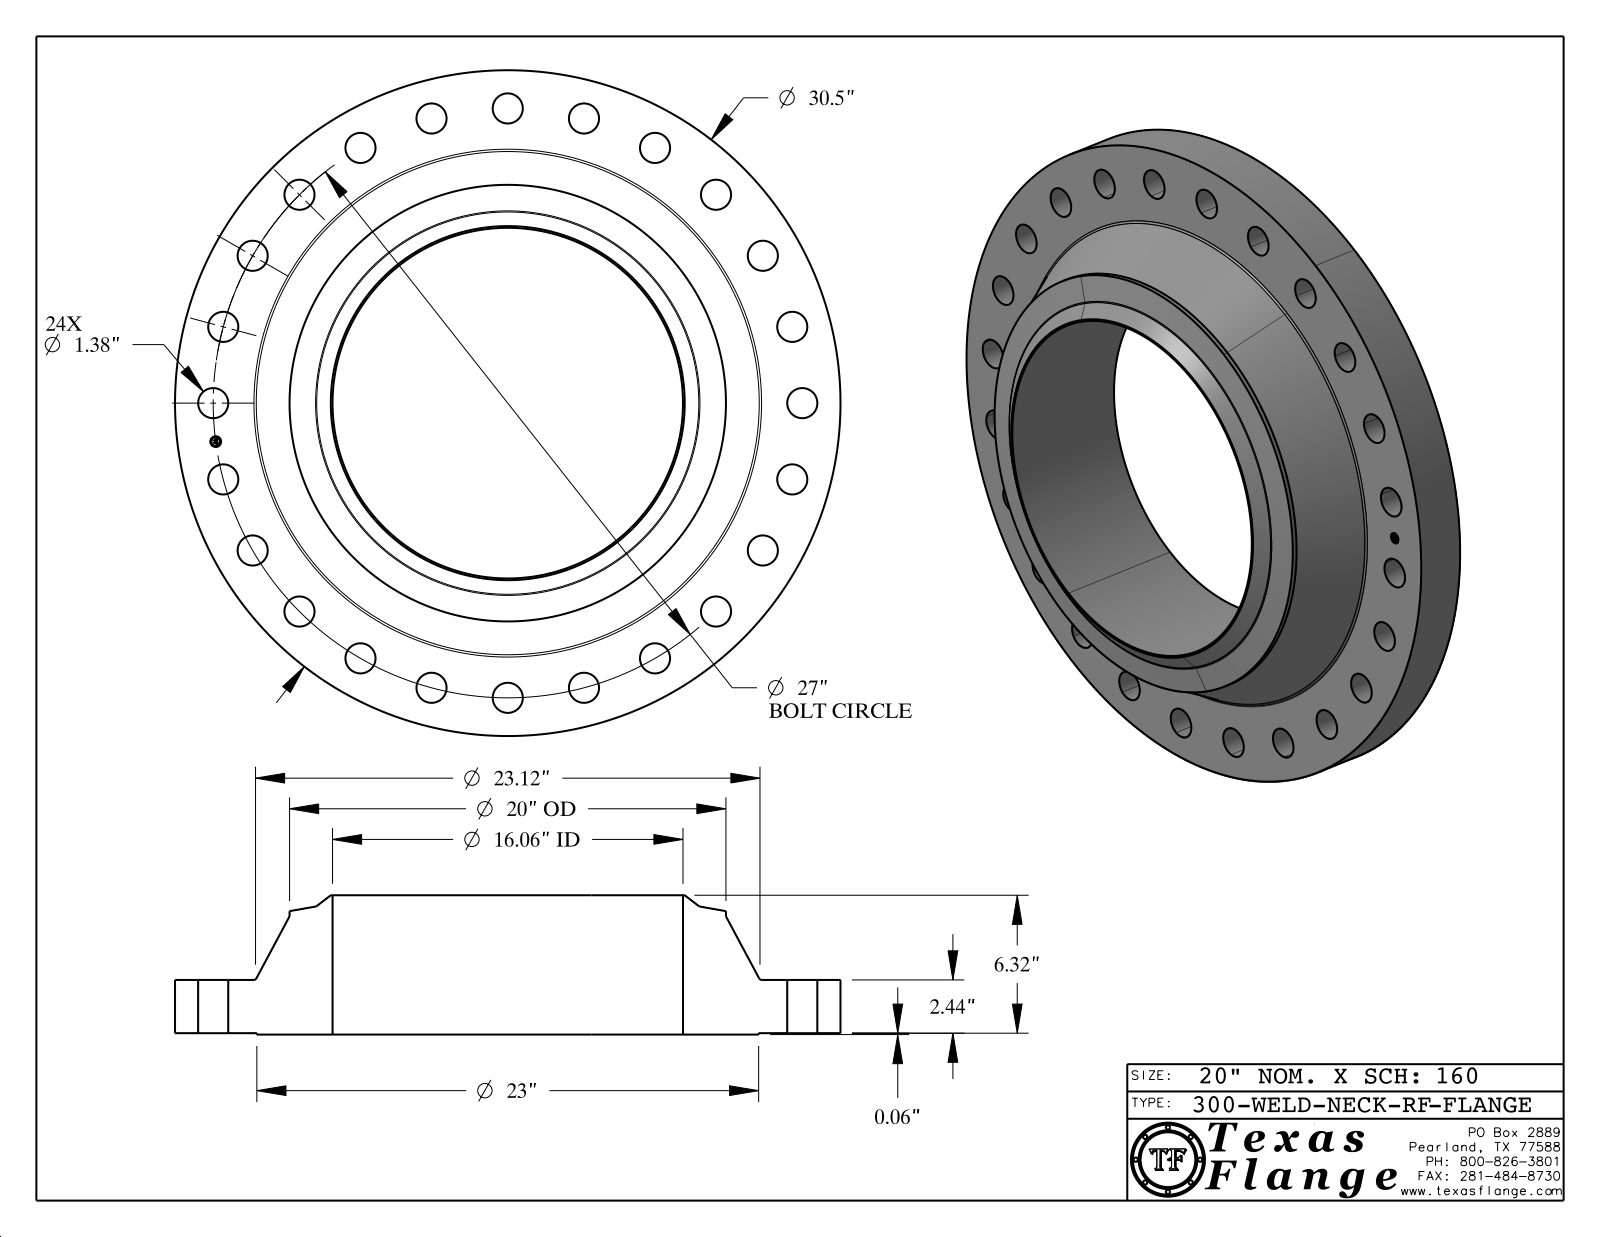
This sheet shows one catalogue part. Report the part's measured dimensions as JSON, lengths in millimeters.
{"part_name": "300-WELD-NECK-RF", "step_written_by": "CATIA V5 STEP AP214 (AUTOMOTIVE_DESIGN)", "units": "millimeters", "bodies": {"solids": 1, "faces": 455, "planar": 369, "cylindrical": 76, "other": 10}, "overall_size": [774.7, 774.7, 162.1], "volume_mm3": 28560000, "surface_area_mm2": 1252000, "round_holes": [[35.1, 24], [12.6, 1], [408, 1]], "round_bosses_or_shafts": [[0.8, 8], [774.7, 1], [584.2, 1], [508, 1], [9.9, 1]], "face_to_face_distances": [62, 1.6, 63.6, 162.1, 160.5, 98.6, 63.2, 61.6, 0.4, 98.9], "hole_center_spacings": [342.9, 89.5, 177.5, 262.5, 417.5, 633.6, 679.9, 544.1]}
